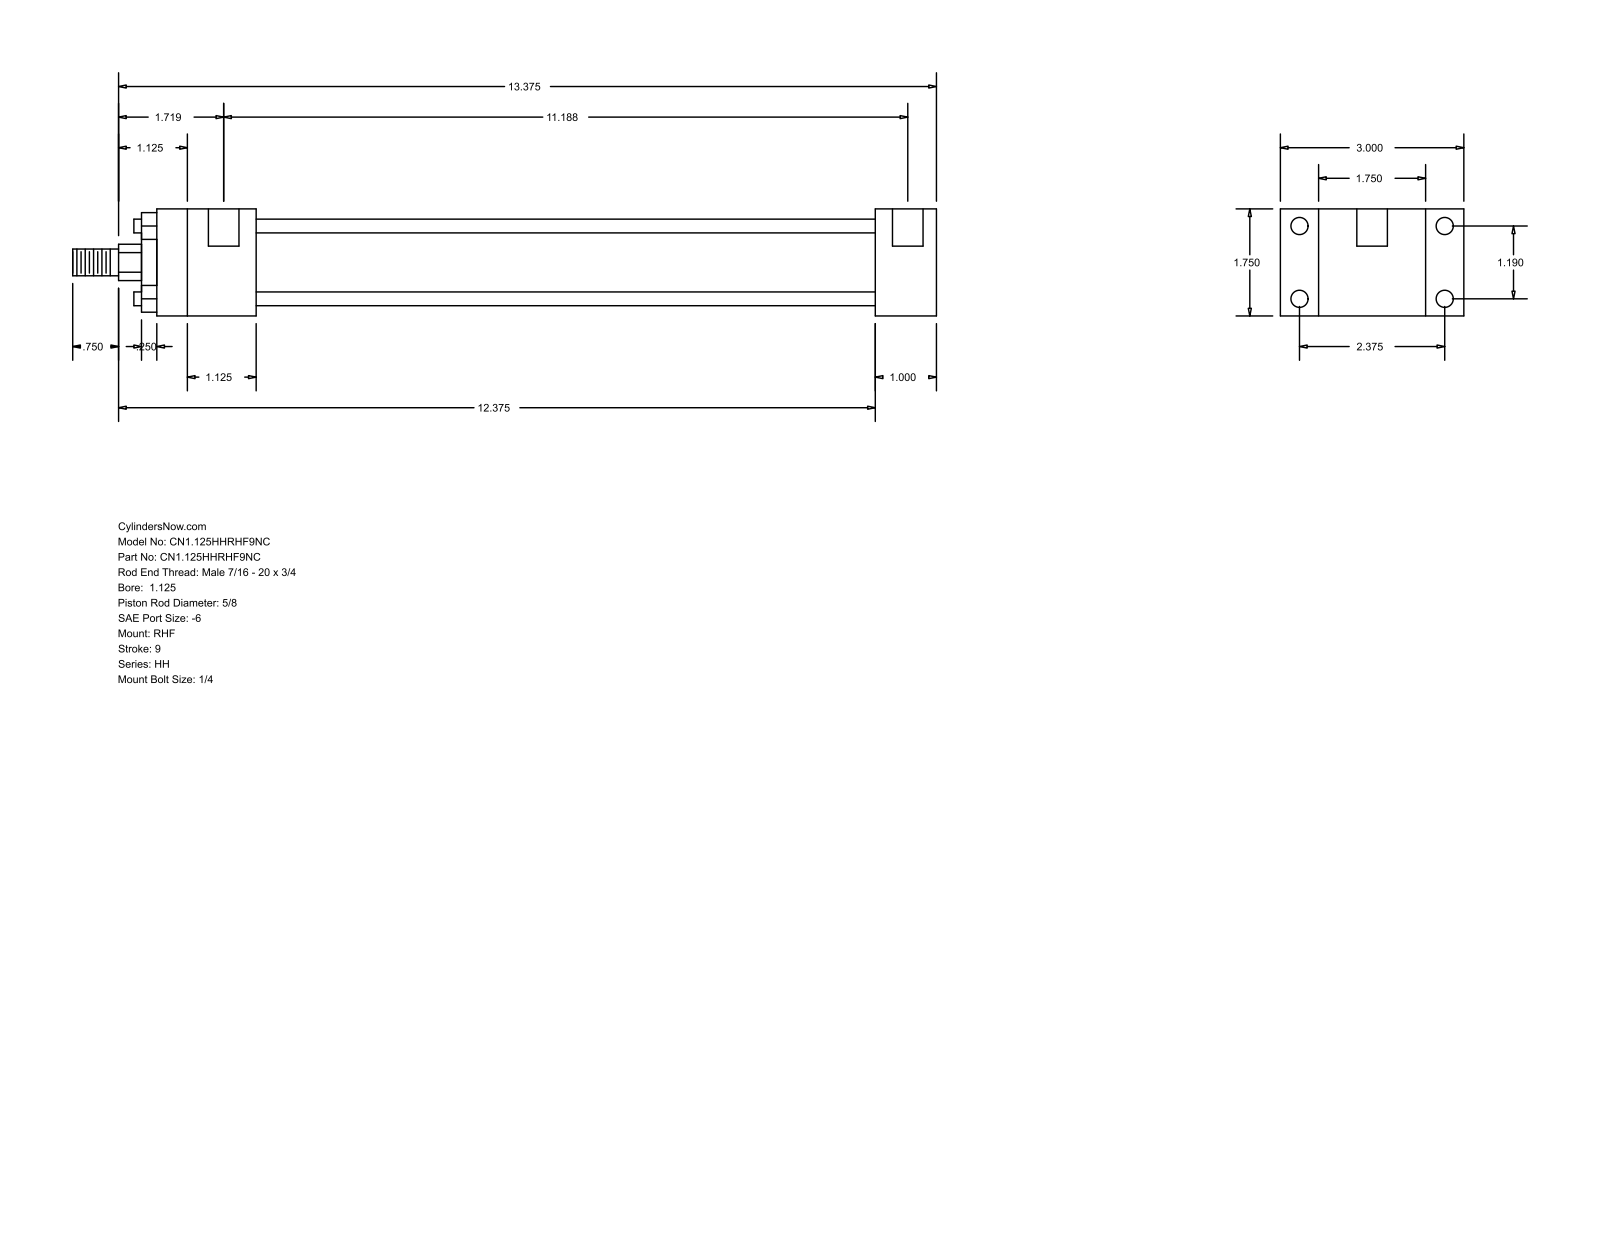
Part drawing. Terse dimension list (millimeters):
name: HH_RHF__0112_0.625
written by: GSSL Pune (CONFIG_CONTROL_DESIGN)
unit: mm
bodies: 0 solids, 88 faces (60 planar, 28 cylindrical, 0 other)
size: 358.77 × 76.2 × 44.45
holes: 4× ⌀5.56, 4× ⌀7.14, 2× ⌀12.7
bosses: 4× ⌀5.71, 1× ⌀34.92, 1× ⌀28.57, 1× ⌀15.88, 1× ⌀11.11
rounds: 1× R7.54
face distances: 44.46, 15.87, 60.33, 25.41, 76.2, 257.17, 282.58, 41.27, 298.44, 323.85
hole spacings: 30.22, 60.32, 67.47, 280.99, 3.17, 284.16
